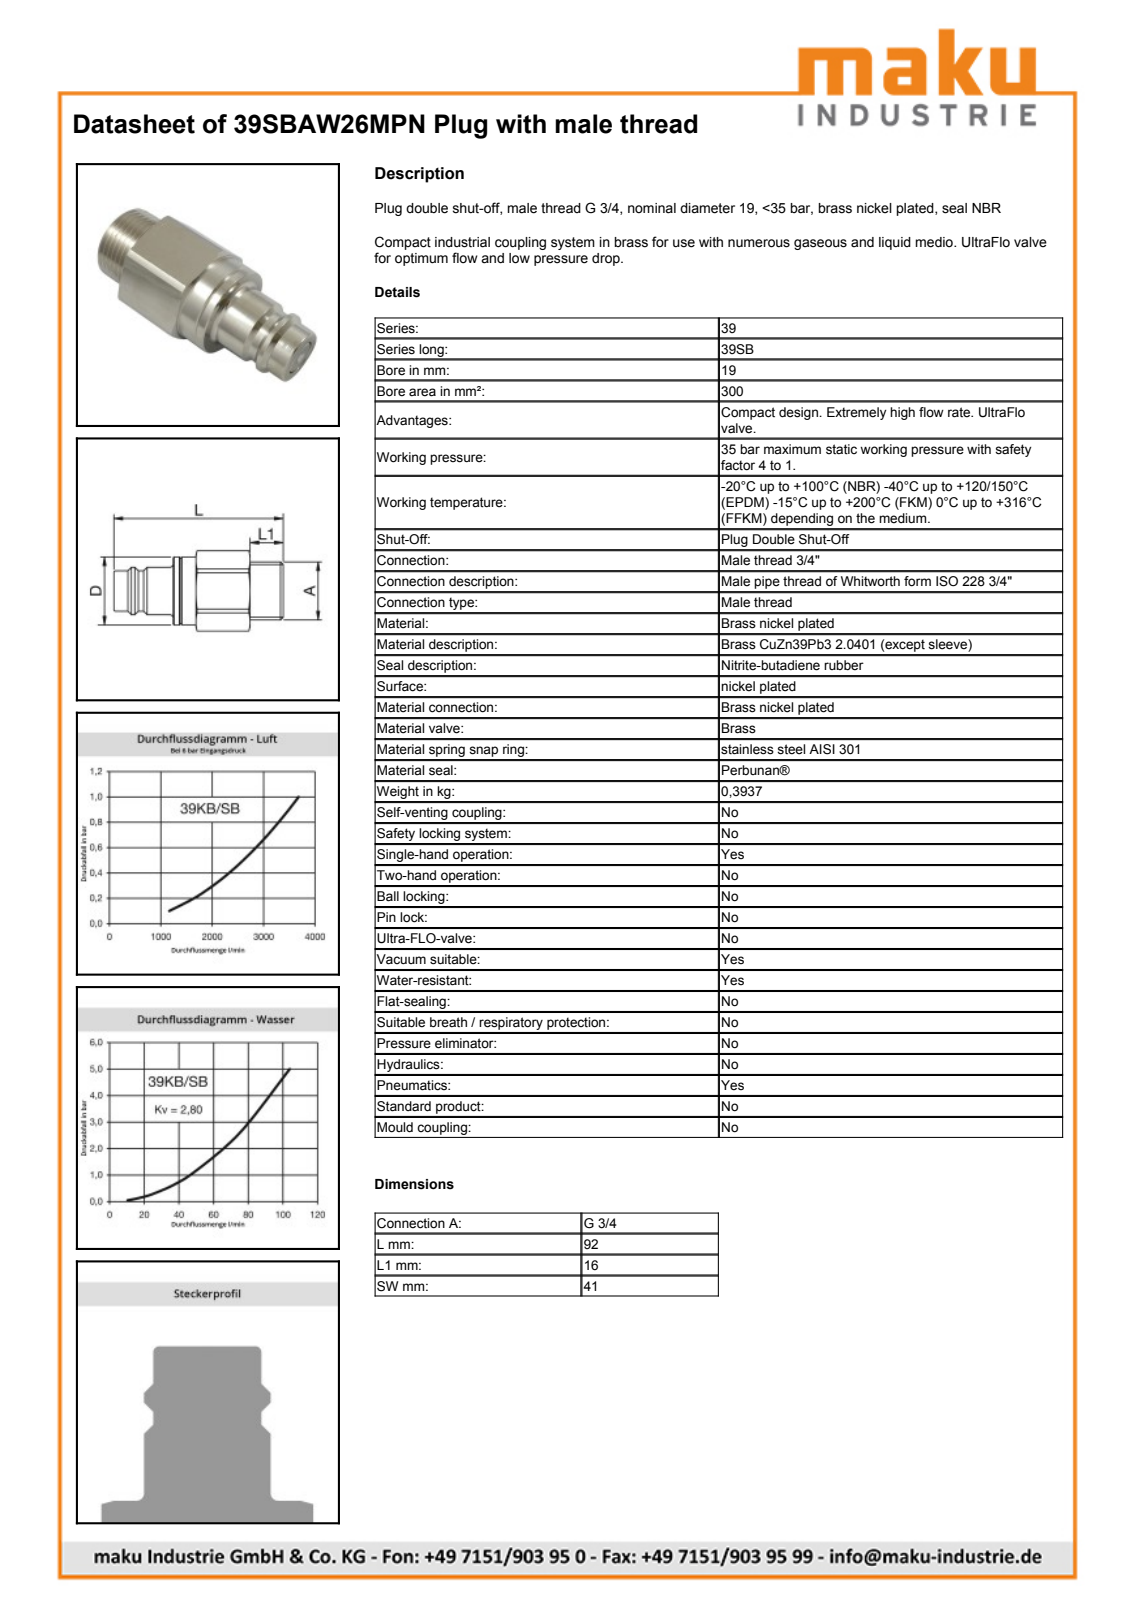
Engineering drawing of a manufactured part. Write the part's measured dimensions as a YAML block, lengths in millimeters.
part_name: "D104951"
step_written_by: "Autodesk Inventor 2011 (AUTOMOTIVE_DESIGN)"
units: millimeters
bodies: {solids: 1, faces: 51, planar: 13, cylindrical: 15, other: 23}
overall_size: [94, 45.95, 41.96]
volume: 86293
surface_area: 13519
round_holes:
  - {diameter: 35, count: 1}
round_bosses_or_shafts:
  - {diameter: 39, count: 1}
  - {diameter: 38.8, count: 1}
  - {diameter: 33, count: 1}
  - {diameter: 27.2, count: 1}
  - {diameter: 26.44, count: 1}
  - {diameter: 23.15, count: 1}
partial_cylinders:
  - {radius: 22.98, count: 1}
face_to_face_distances: [40.98, 41, 41.02, 16, 44, 60, 34, 78, 94, 47]
